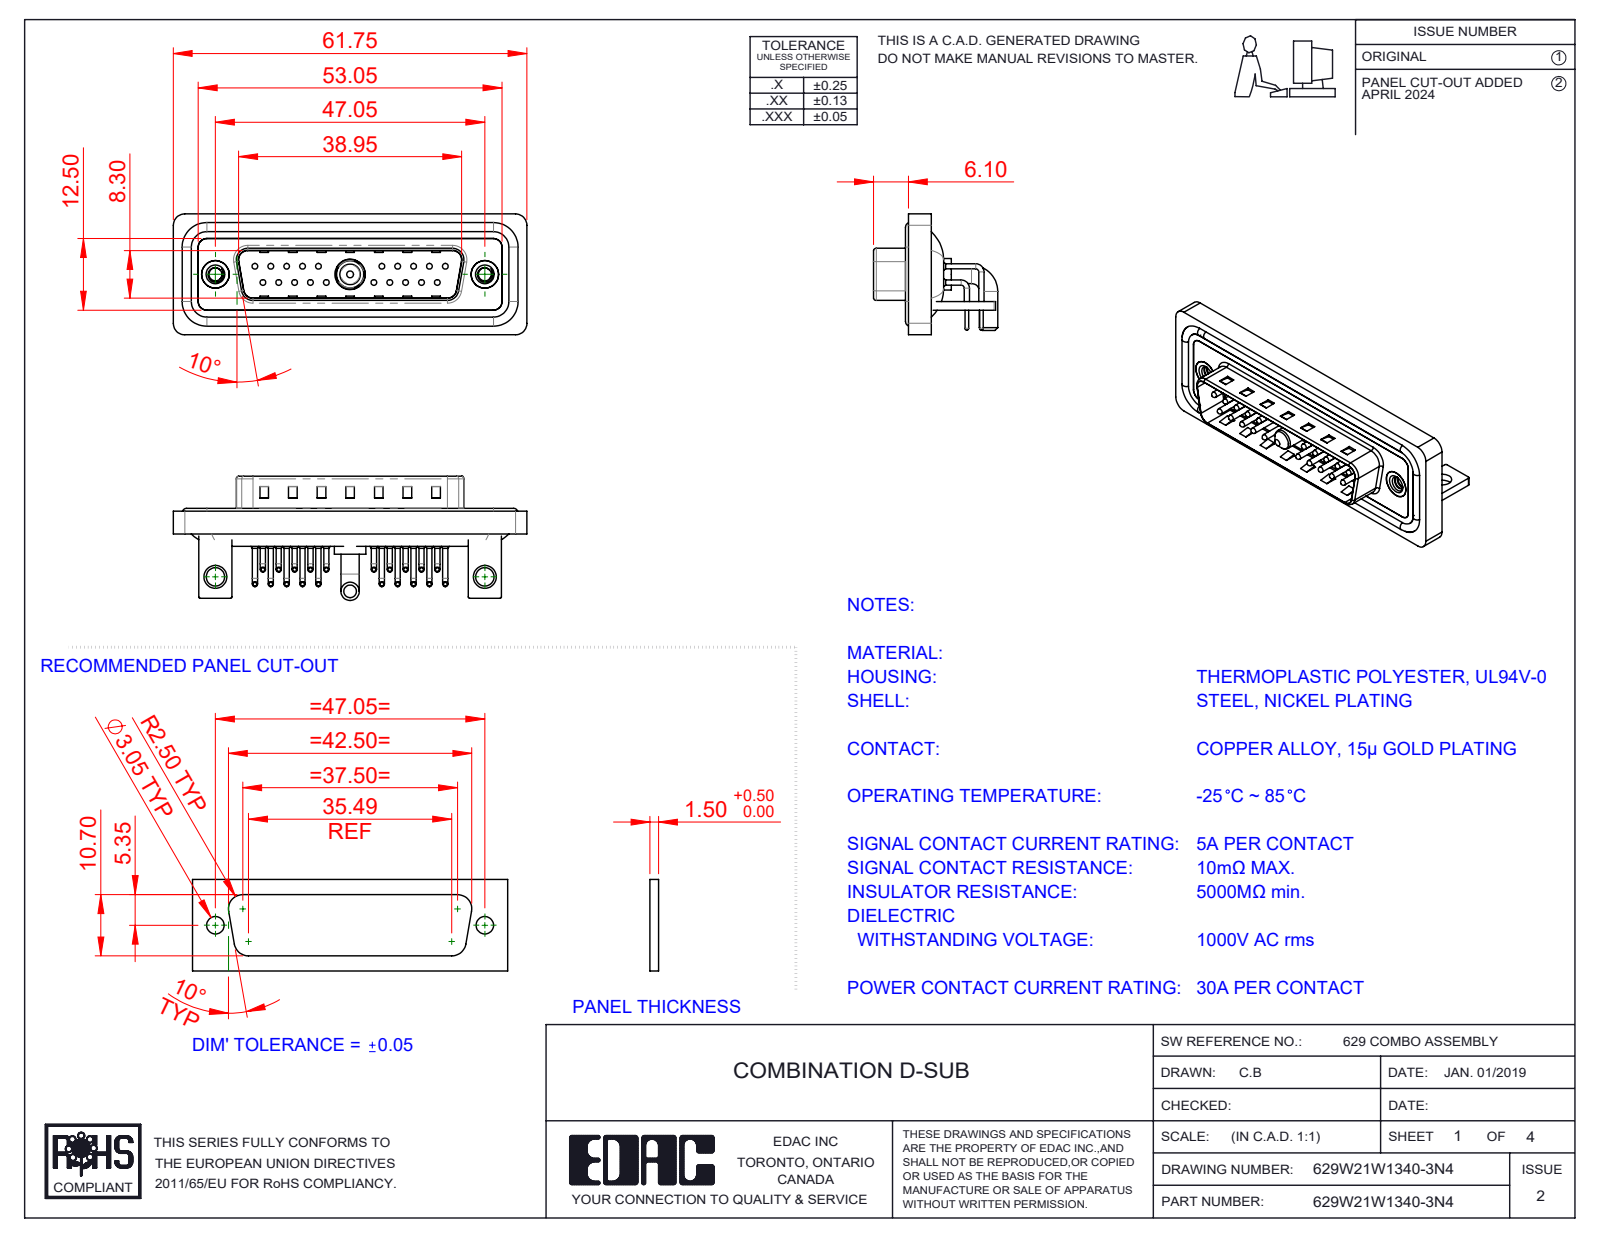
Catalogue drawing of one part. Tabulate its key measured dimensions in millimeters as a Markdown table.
| quantity | value |
| --- | --- |
| part name | 629Combo Shell Rear_25 Contacts; 629Combo Stabilizer Bracket; 629Combo Housing_21W1; 629Combo Waterproof Housing_25 Contacts (+6 more) |
| STEP written by | SolidWorks 2023 (CONFIG_CONTROL_DESIGN) |
| units | millimeters |
| bodies | 31 solids, 2766 faces (1519 planar, 947 cylindrical, 300 other) |
| overall size | 61.75 × 21.7 × 21.1 |
| volume | 7 724 mm³ |
| surface area | 13 326 mm² |
| round holes (diameter × count) | 0.75 × 20, 1.6 × 20, 2 × 20, 2.26 × 2, 3.2 × 2, 4 × 2, 4.8 × 2, 5 × 2, 4.85 × 1, 5.3 × 1 |
| round bosses / shafts (diameter × count) | 0.9 × 40, 1.5 × 20, 1 × 20, 0.65 × 20, 1.6 × 4, 4.9 × 2, 3.2 × 2, 5.5 × 1 |
| partial cylindrical surfaces (radius × count) | 1.01 × 20, 2 × 19, 1.5 × 18, 0.25 × 16, 0.5 × 9, 1.6 × 8, 0.6 × 4, 0.65 × 4 |
| main face-to-face distances | 0.4, 0.8, 2.1, 2.9, 1.5, 1.1, 4.1, 1.6, 4.5, 3.7 |
| hole center spacings | 3.16, 2.77, 5.54, 8.31, 5.04, 19.39, 20.97, 22.16 |
